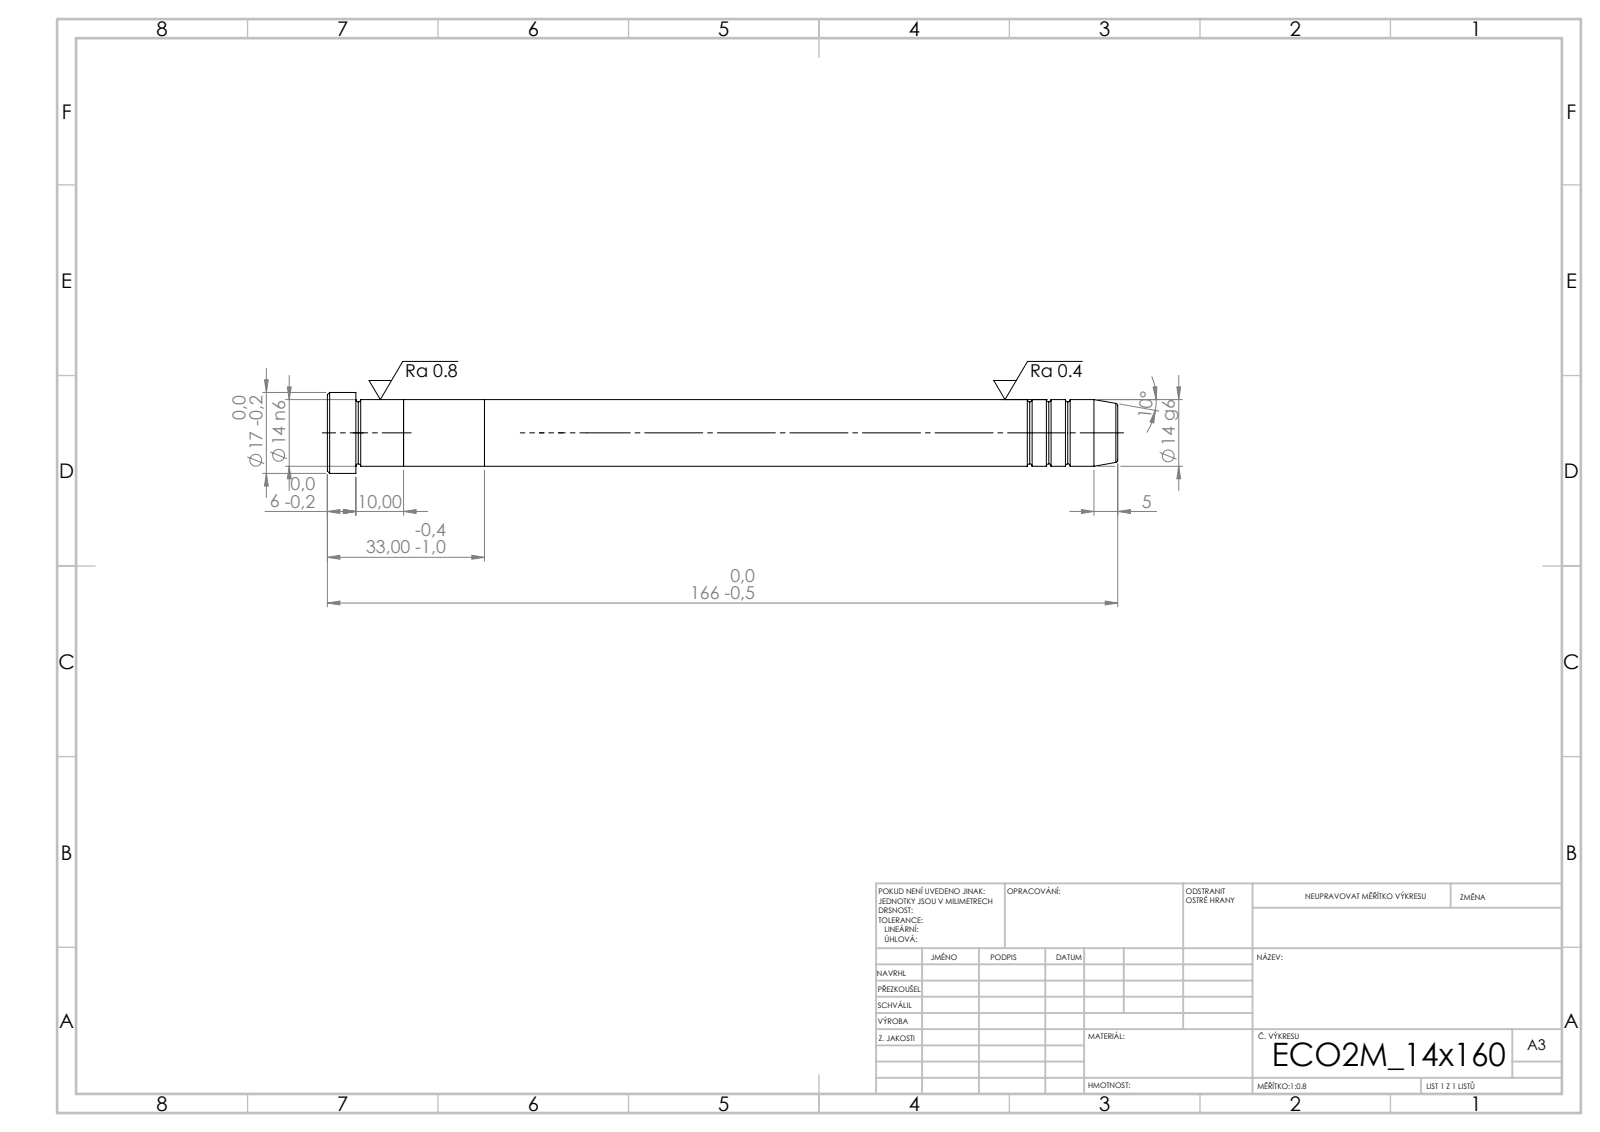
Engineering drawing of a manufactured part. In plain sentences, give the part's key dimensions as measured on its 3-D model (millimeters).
Its 3-D file was written by "SolidWorks 2019 (CONFIG_CONTROL_DESIGN)". It is 3 solids with 43 faces: 7 planar, 14 cylindrical and 22 other. Overall it measures 166 by 17 by 17 millimeters. Its volume is 25 824 cubic millimeters and its surface area 8 447 square millimeters. Round bosses or shafts: 1 of diameter 17, 1 of diameter 14. The main face-to-face distances are 17, 33, 16, 133, 150, 166, 160, 27, 10, 6.
